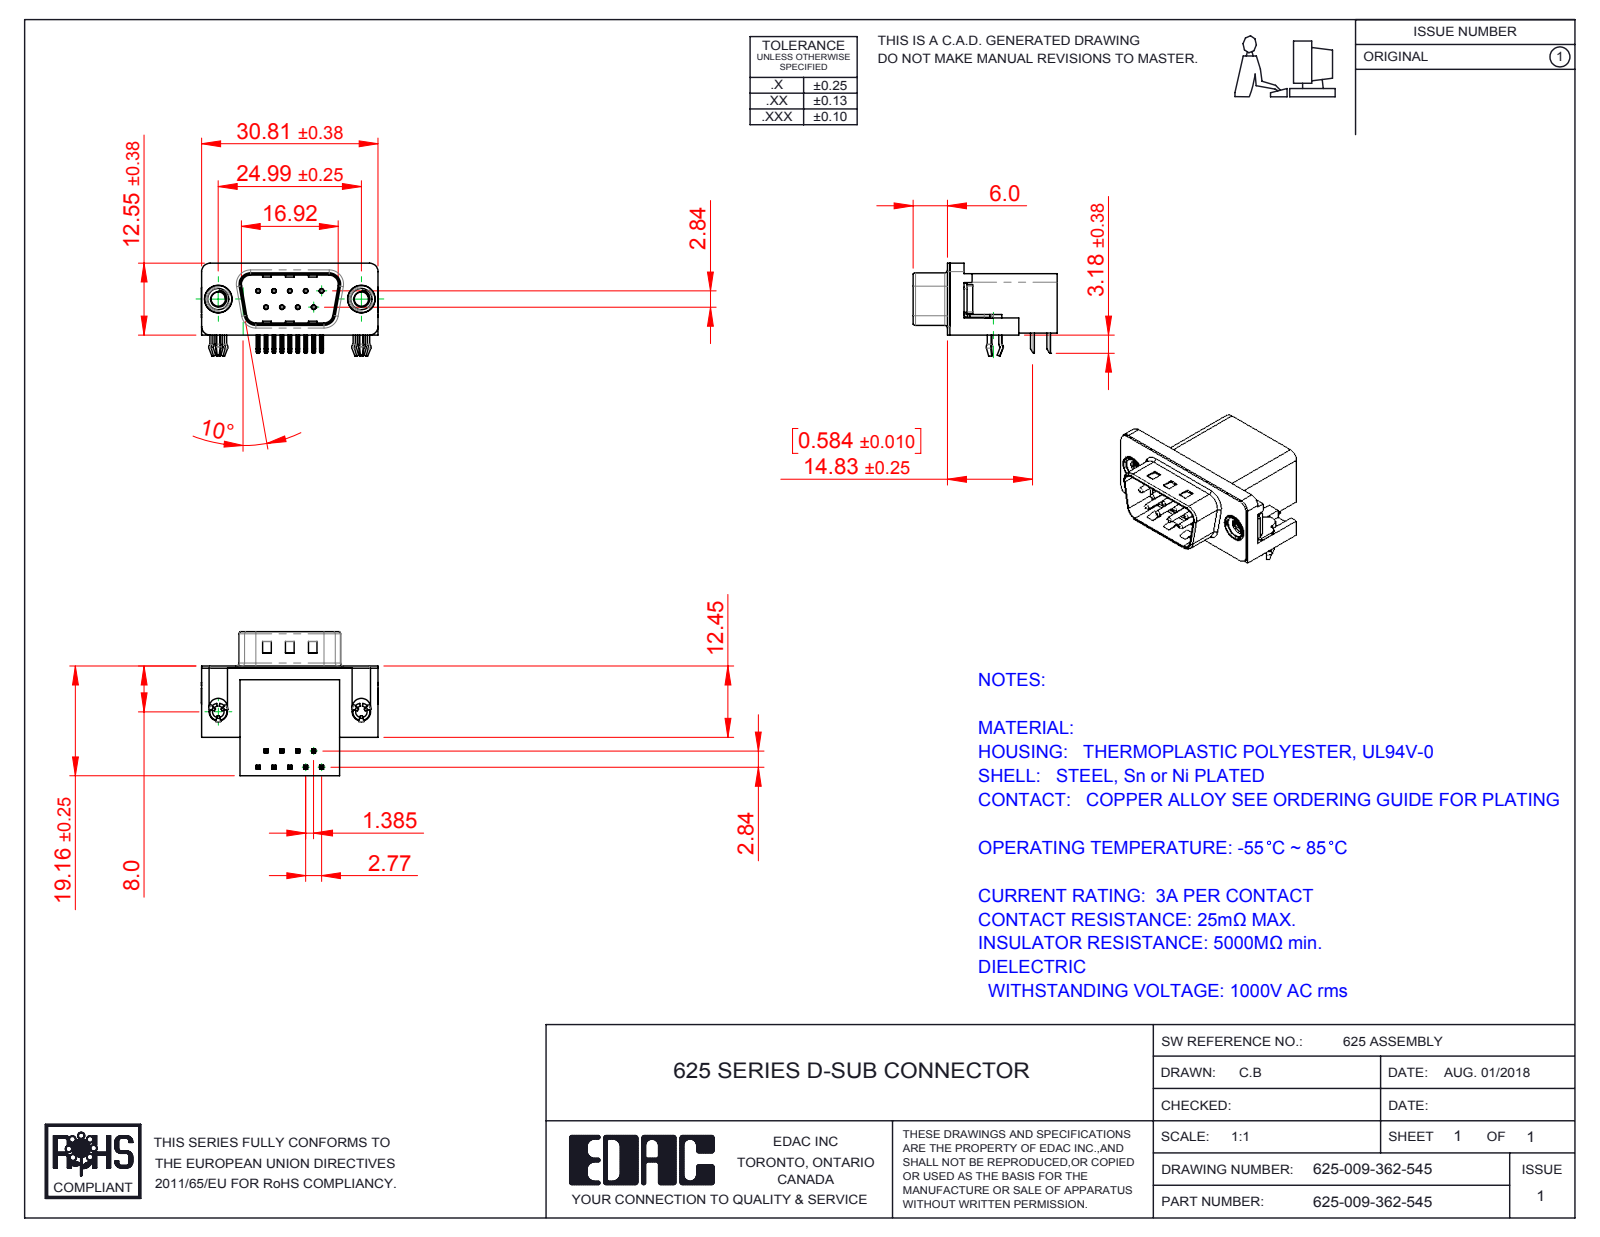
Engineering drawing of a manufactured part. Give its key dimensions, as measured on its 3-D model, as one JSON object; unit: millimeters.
{"part_name": "625 Housing_9 Socket; 625 Contact Bottom; 625 Contact Top; 625 Shell_9 Socket (+3 more)", "step_written_by": "SolidWorks 2016 (CONFIG_CONTROL_DESIGN)", "units": "millimeters", "bodies": {"solids": 15, "faces": 1097, "planar": 611, "cylindrical": 327, "other": 159}, "overall_size": [30.89, 25.16, 16.25], "volume_mm3": 4479, "surface_area_mm2": 5016, "round_holes": [[0.35, 9], [0.8, 9], [2, 2], [2.5, 2], [4, 2], [4.8, 2], [5, 2]], "round_bosses_or_shafts": [[0.75, 9], [4.9, 2], [4.75, 2], [3.9, 2], [3, 2]], "partial_cylinders_radius": [[0.25, 48], [0.12, 18], [1, 16], [0.5, 9], [1.5, 8], [1.6, 8], [0.9, 4], [2, 4]], "face_to_face_distances": [0.4, 10.34, 18.76, 19.16, 2.9, 16.26, 2.5, 0.35, 10.69, 6.7], "hole_center_spacings": [3.16, 2.77, 5.54, 5.03, 5.04, 8.31, 7.48, 7.49]}
